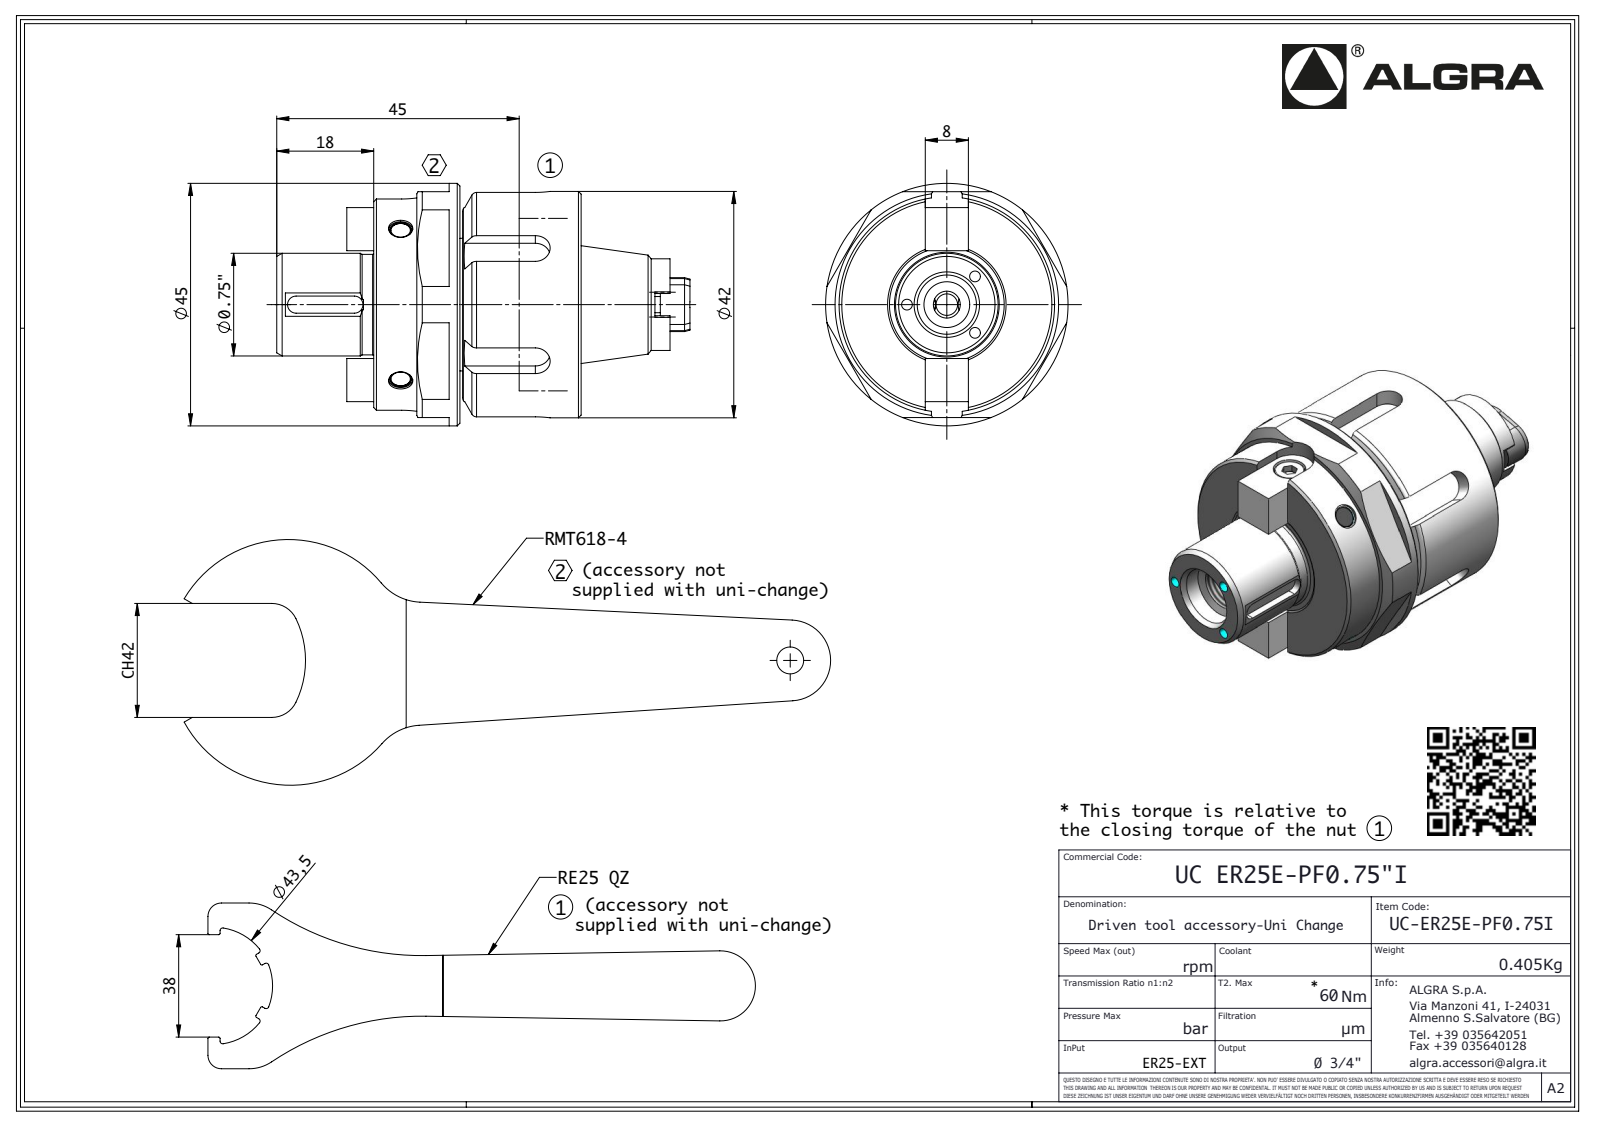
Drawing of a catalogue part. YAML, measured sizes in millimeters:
part_name: "UC-ER25E-PF0.75I"
step_written_by: "SolidWorks 2016 (AUTOMOTIVE_DESIGN)"
units: millimeters
bodies: {solids: 0, faces: 143, planar: 85, cylindrical: 36, other: 22}
overall_size: [73, 45, 45]
round_holes:
  - {diameter: 2.5, count: 2}
  - {diameter: 6, count: 2}
  - {diameter: 5, count: 1}
  - {diameter: 8.5, count: 1}
  - {diameter: 11, count: 1}
  - {diameter: 30.5, count: 1}
  - {diameter: 32.4, count: 1}
round_bosses_or_shafts:
  - {diameter: 45, count: 1}
  - {diameter: 42, count: 1}
  - {diameter: 40, count: 1}
  - {diameter: 19.05, count: 1}
  - {diameter: 18.65, count: 1}
  - {diameter: 17, count: 1}
partial_cylinders:
  - {radius: 0.24, count: 4}
  - {radius: 2.75, count: 3}
  - {radius: 1.59, count: 2}
  - {radius: 3.81, count: 2}
  - {radius: 4, count: 1}
  - {radius: 5.05, count: 1}
face_to_face_distances: [16, 8, 13, 2.95, 38.95, 22.5, 38.5, 36, 9.5, 25.5]
hole_center_spacings: [5.25, 10.5]
